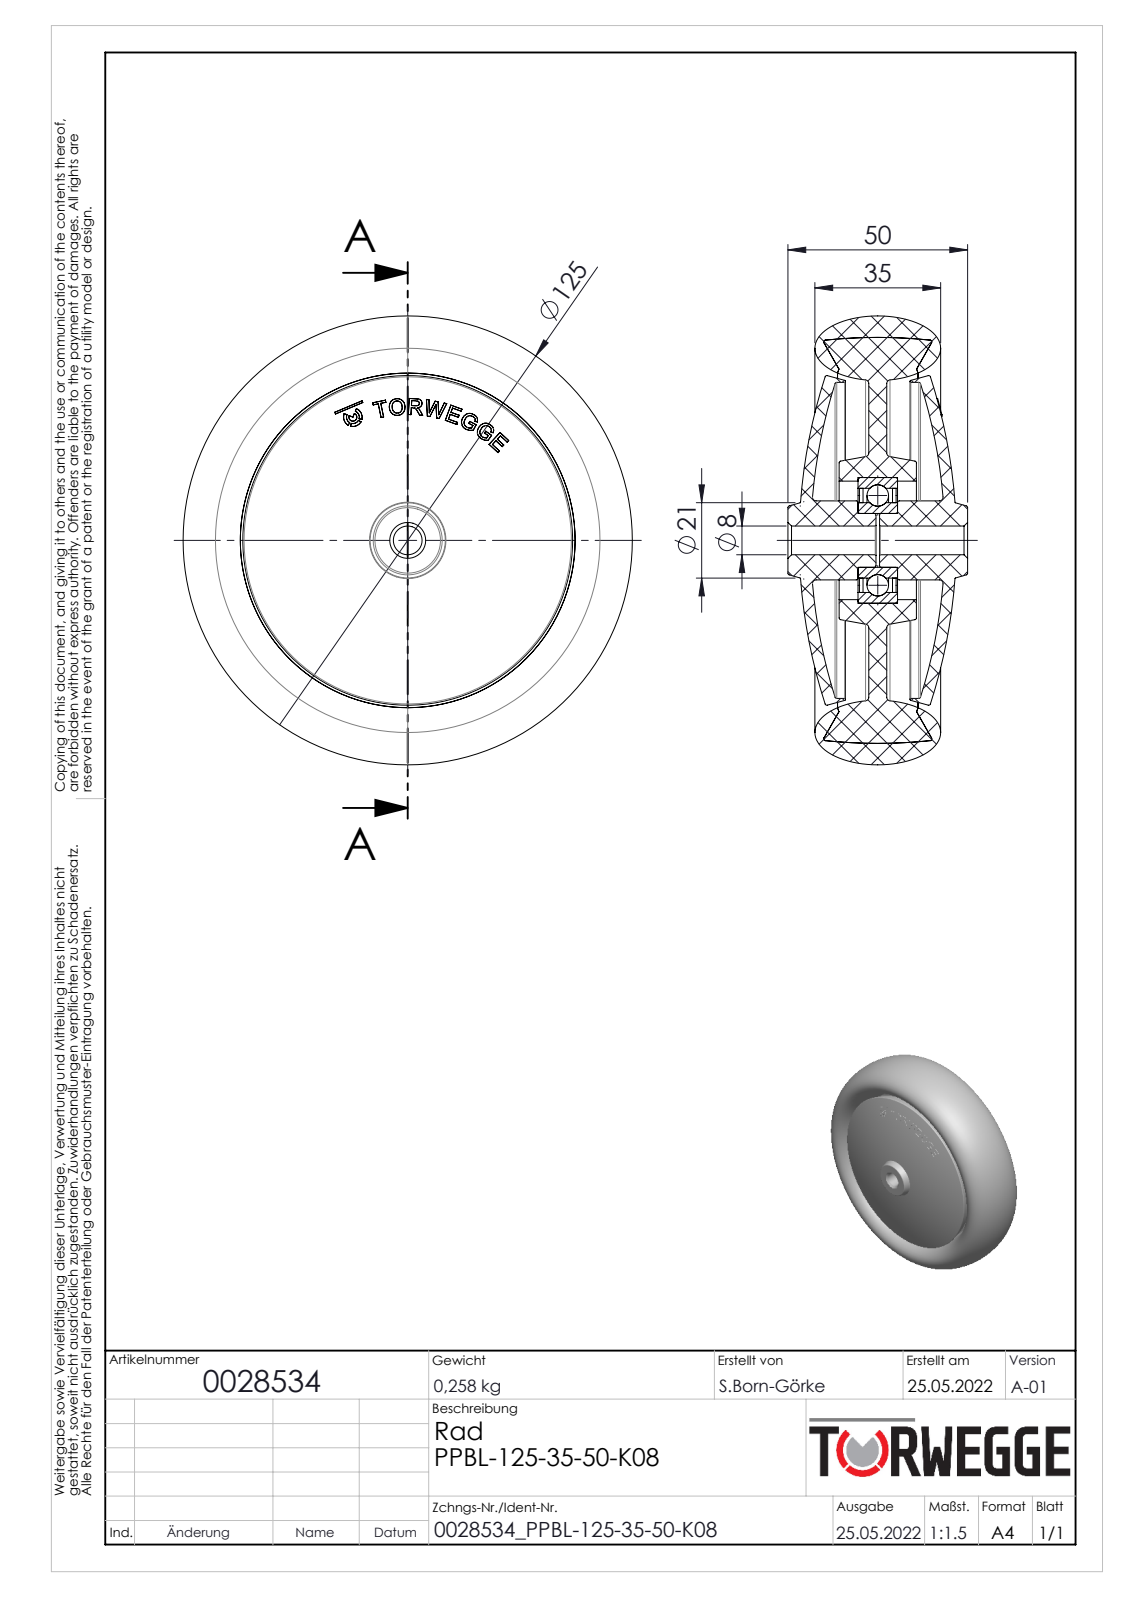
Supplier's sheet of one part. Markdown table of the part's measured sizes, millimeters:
| quantity | value |
| --- | --- |
| part name | 0028534 |
| STEP written by | SolidWorks 2018 (AUTOMOTIVE_DESIGN) |
| units | millimeters |
| bodies | 8 solids, 428 faces (22 planar, 42 cylindrical, 364 other) |
| overall size | 125 × 125 × 50 |
| volume | 267 763 mm³ |
| surface area | 84 145 mm² |
| round holes (diameter × count) | 8 × 1, 21 × 1, 29 × 1, 33 × 1, 35 × 1, 88 × 1 |
| round bosses / shafts (diameter × count) | 22 × 1, 15 × 1 |
| main face-to-face distances | 5, 3, 8, 5.25, 8.25, 13.25, 16.25, 1, 11, 5.65 |
